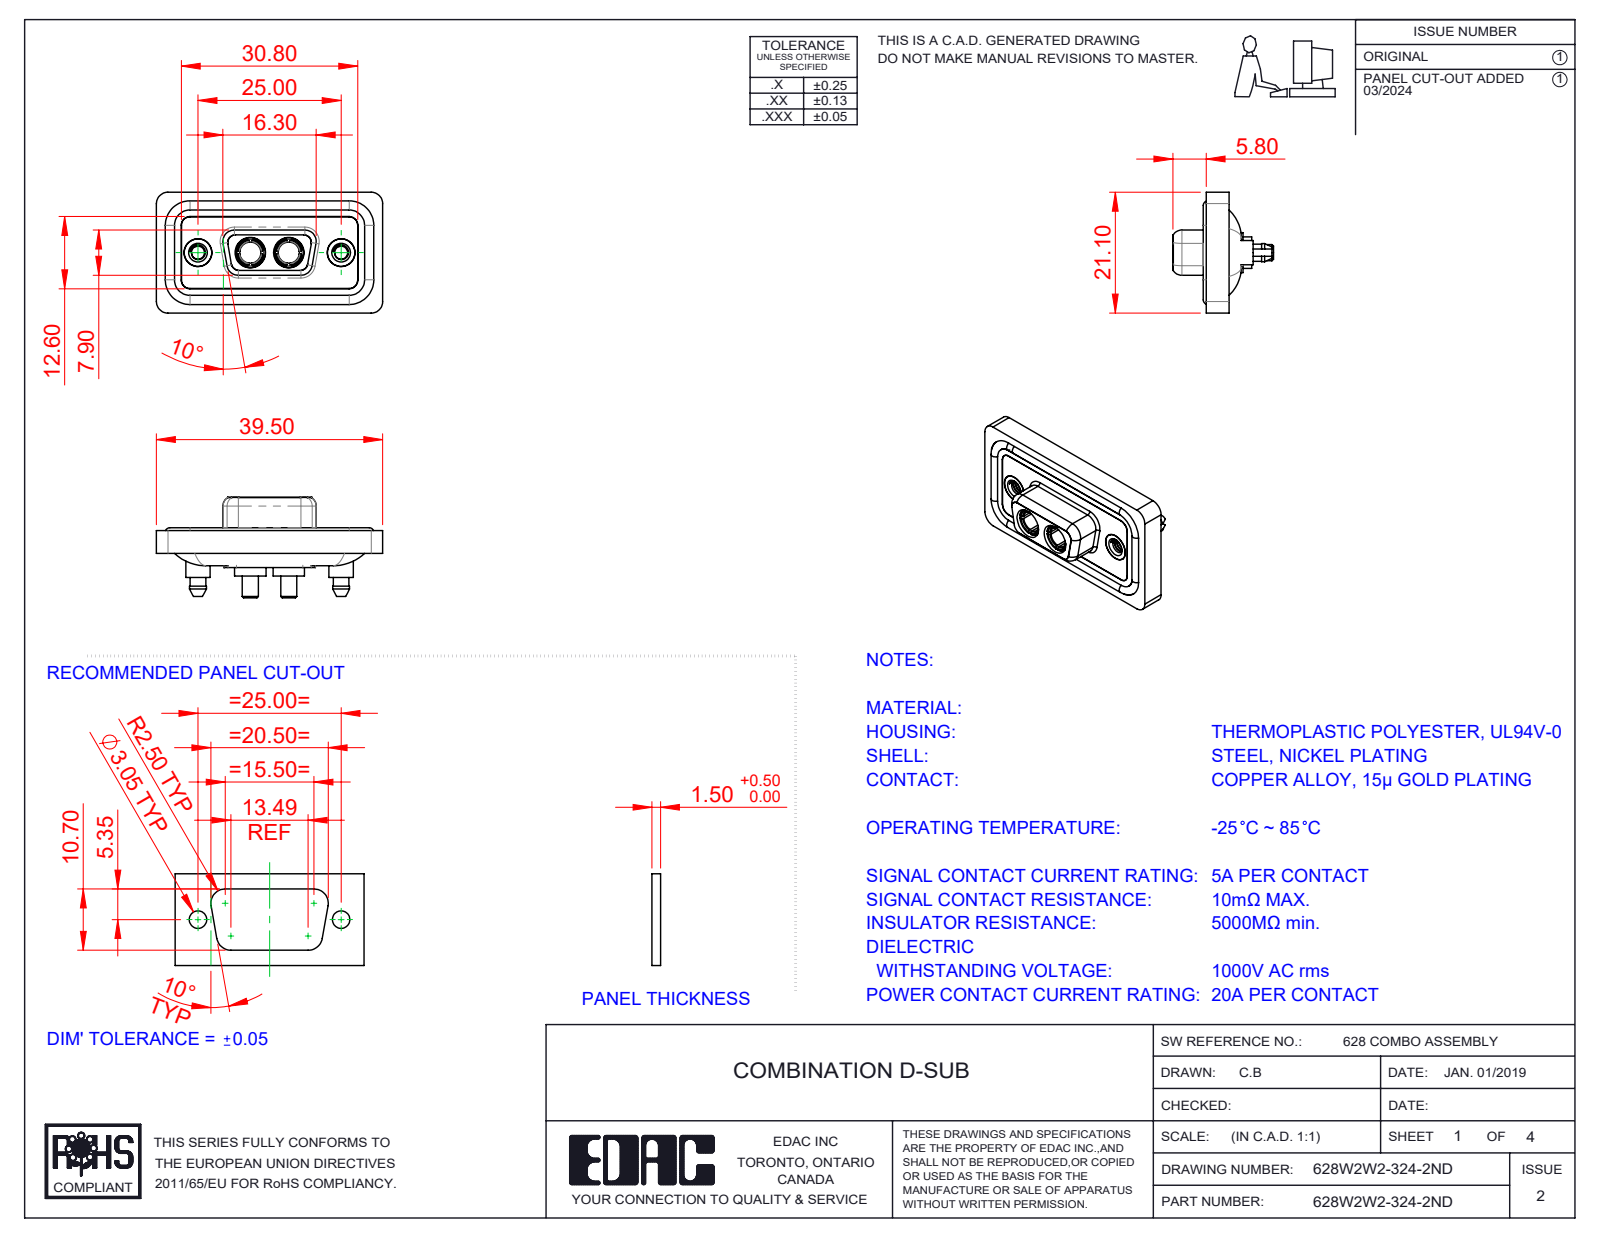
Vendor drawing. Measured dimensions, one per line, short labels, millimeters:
name: 628Combo Housing_2W2; 628Combo Shell Front_09 Contacts; Power Socket_20A S; 628Combo Shell Rear_09 Contacts (+3 more)
written by: SolidWorks 2023 (CONFIG_CONTROL_DESIGN)
unit: mm
bodies: 11 solids, 600 faces (179 planar, 282 cylindrical, 139 other)
size: 39.5 × 21.1 × 17.55
volume: 4 848 mm³; area: 7 975 mm²
holes: 4× ⌀4.85, 2× ⌀2.26, 2× ⌀3.7, 2× ⌀4, 2× ⌀4.05, 2× ⌀5, 2× ⌀5.3
bosses: 4× ⌀1.6, 2× ⌀5.5, 2× ⌀5.4, 2× ⌀5.2, 2× ⌀4.96, 2× ⌀4.95, 2× ⌀4.8, 2× ⌀4.75
rounds: 24× R1.5, 18× R2, 10× R1.6, 8× R1.35, 4× R0.25, 4× R0.5, 4× R0.6, 4× R0.65
face distances: 0.4, 1.8, 1.1, 2.9, 1.6, 0.5, 5.65, 7.45, 1.5, 4
hole spacings: 9.14, 15.86, 6.72, 25
